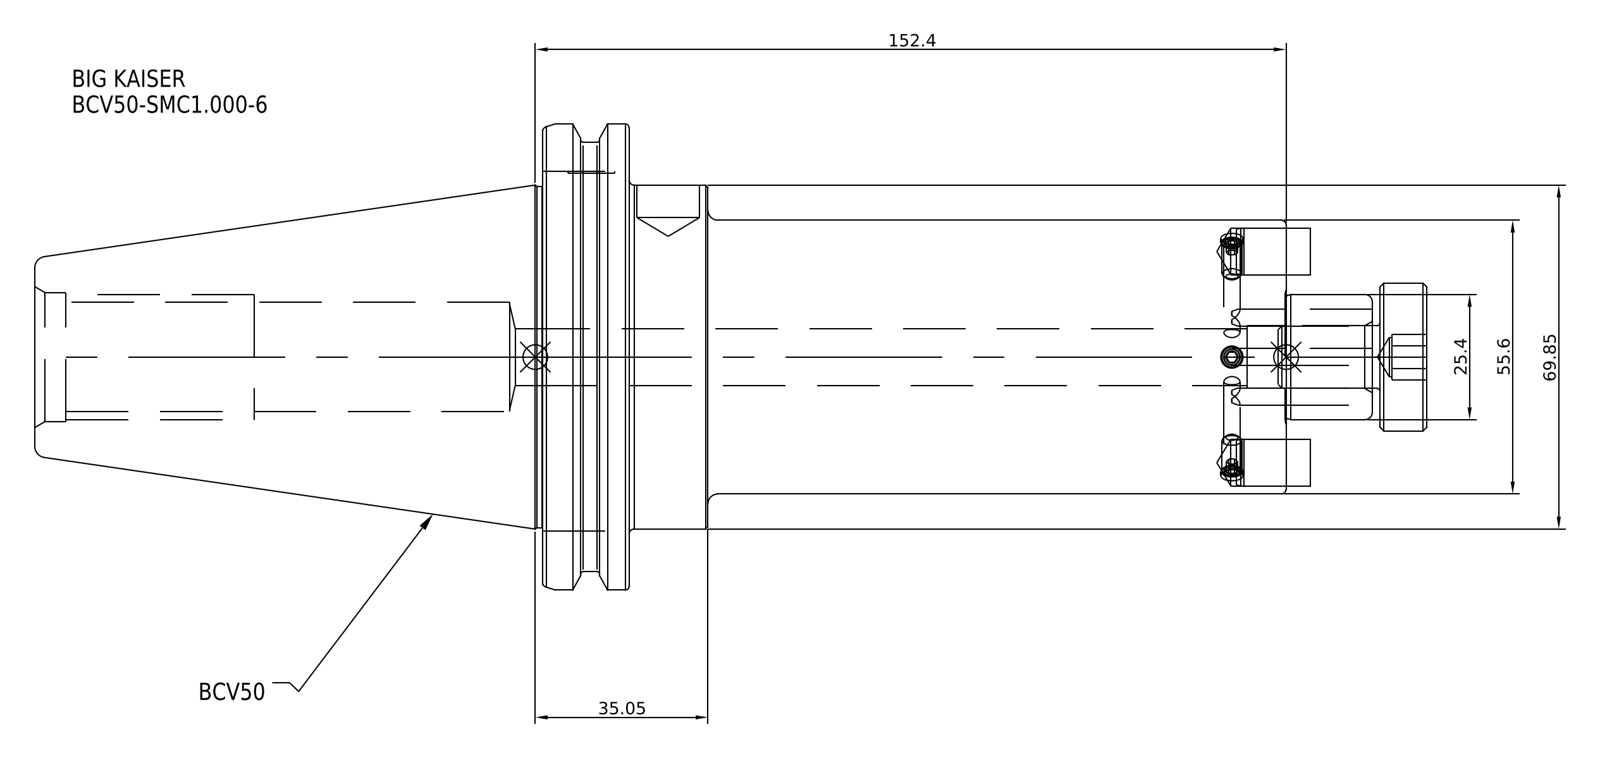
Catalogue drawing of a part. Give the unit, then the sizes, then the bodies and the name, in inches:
Units: inches
Overall size (bounding box): 10.193 × 3.875 × 3.875
Round holes (diameter × count): ⌀0.453 ×1
Round bosses / shafts (diameter × count): ⌀3.875 ×1, ⌀3.594 ×1, ⌀2.75 ×1, ⌀2.189 ×1
Main face-to-face distances: 0.691, 5.25, 5.941, 4.62, 0.63, 1.321, 10, 5.38, 4.75, 4.059
Volume: 43.71 in³ · Surface area: 102.5 in²
Bodies: 1 solid, 38 faces (18 planar, 14 cylindrical, 6 other)
Part name (STEP PRODUCT): BCV50-SMC1_000-6
STEP written by: SolidWorks 2021 (CONFIG_CONTROL_DESIGN)
